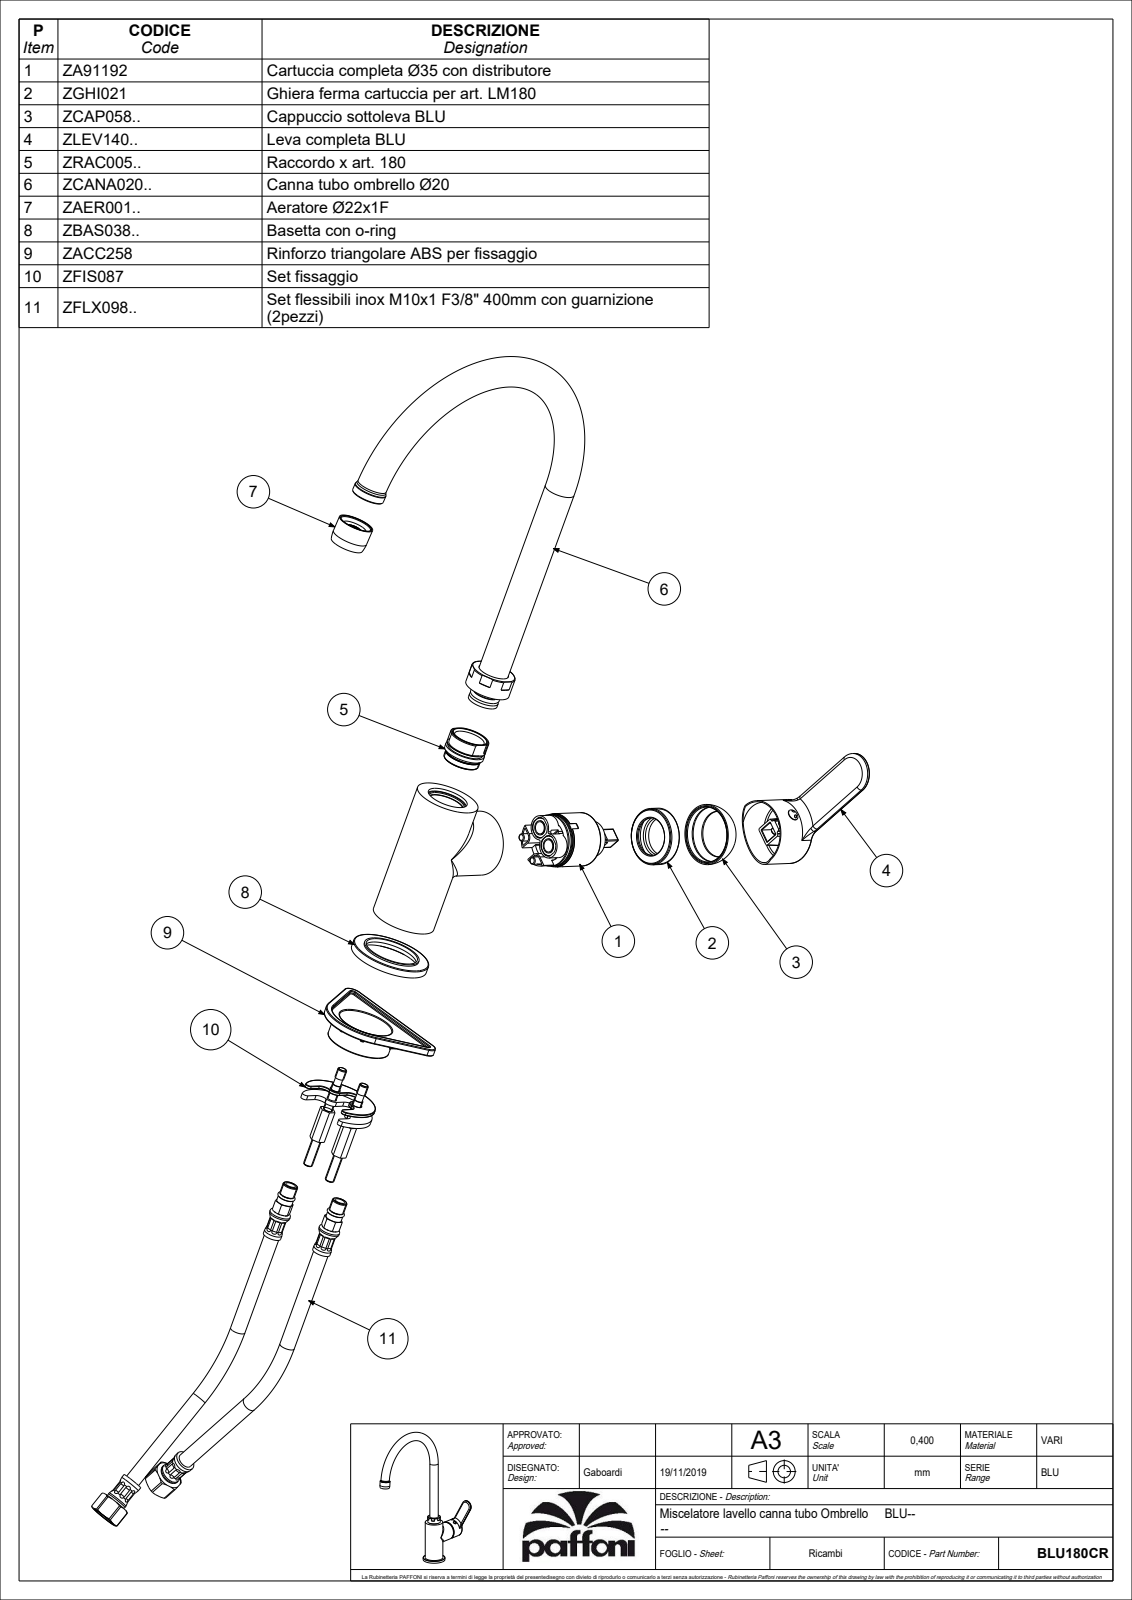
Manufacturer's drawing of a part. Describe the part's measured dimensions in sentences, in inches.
The part is named "BLU180CR". Its 3-D file was written by "CREO PARAMETRIC BY PTC INC, 2020044 (CONFIG_CONTROL_DESIGN)". It is 0 solids with 97 faces: 28 planar, 27 cylindrical and 42 other. Overall it measures 13.591 by 10.78 by 2.952 inches. Round bosses or shafts: 3 of diameter 1.654, 1 of diameter 2.047, 1 of diameter 1.181, 1 of diameter 0.929, 1 of diameter 0.787, 1 of diameter 0.74, 1 of diameter 0.299. Partial cylindrical surfaces (rounded edges, fillets, slot ends): 2 of radius 0.02, 2 of radius 0.098, 2 of radius 0.394, 1 of radius 0.512, 1 of radius 31.496. The main face-to-face distances are 0.197, 3.74, 3.543, 1.102, 4.287, 4.091, 0.547, 0.638, 0.63, 1.142.
